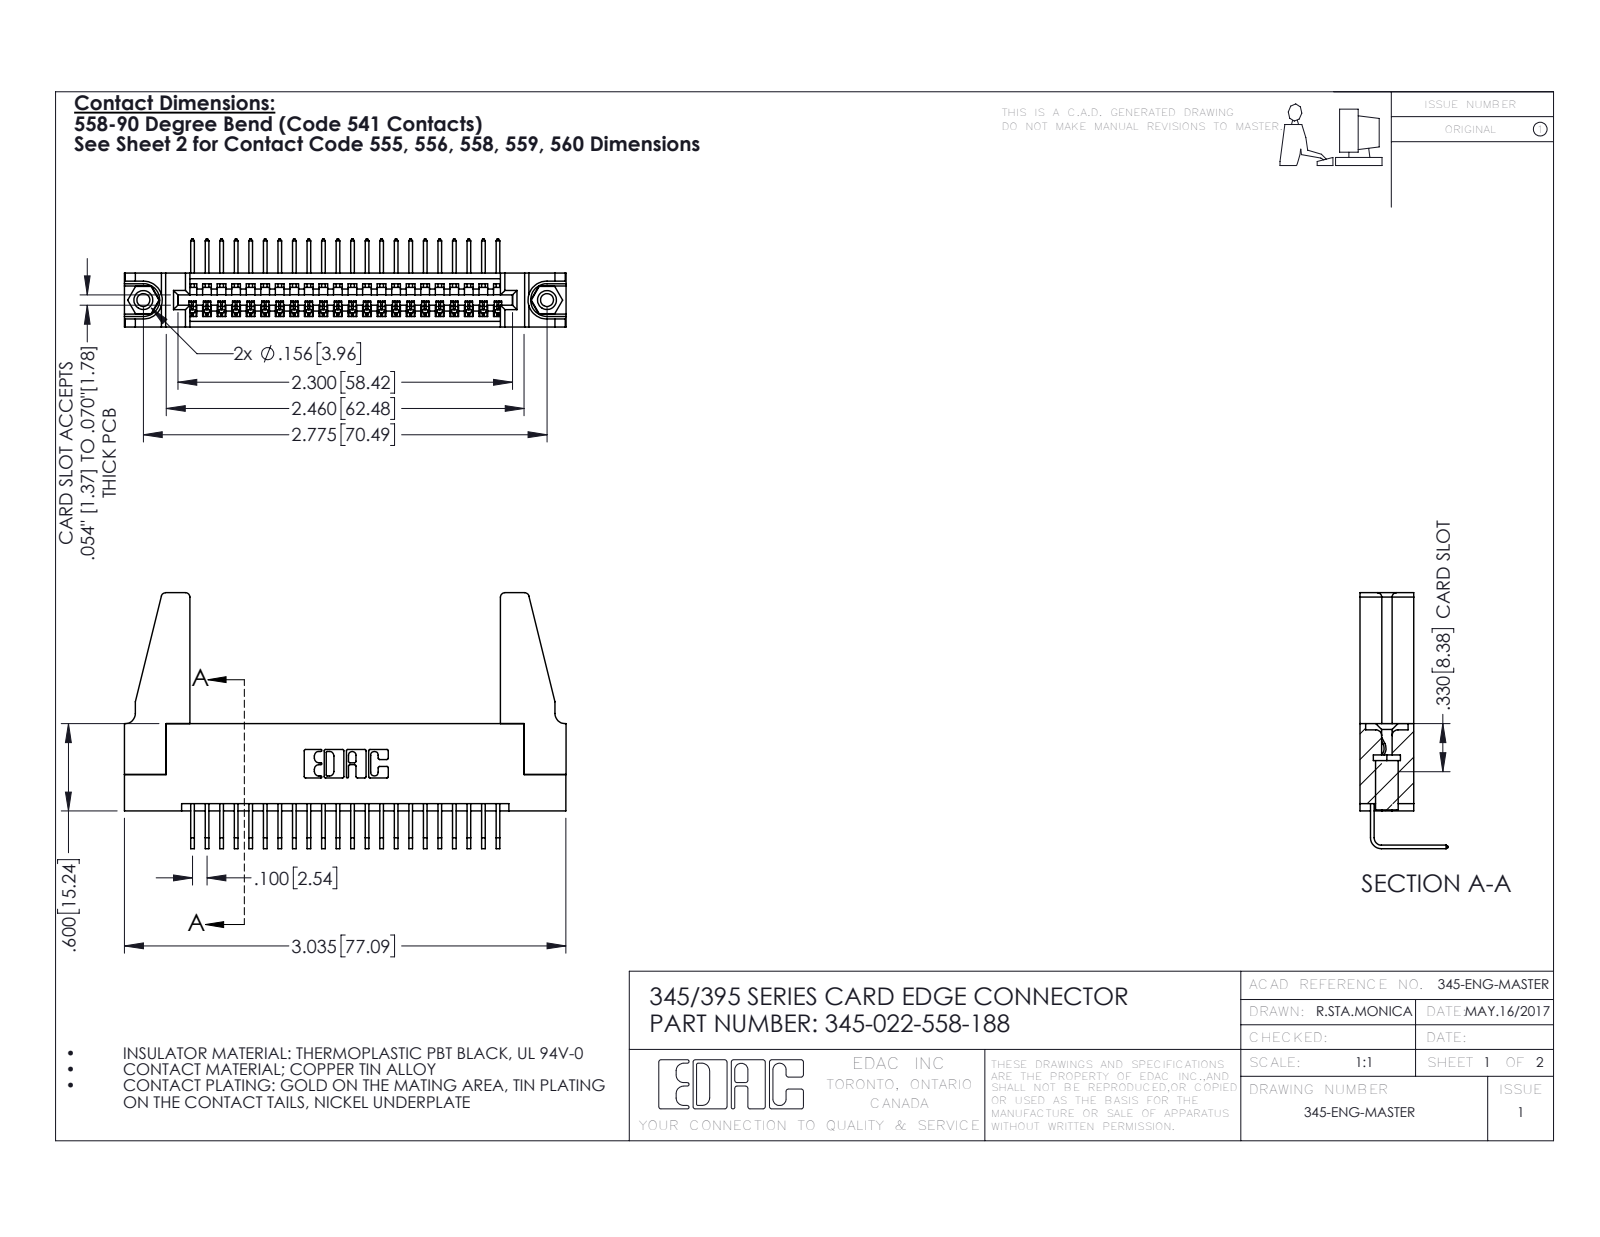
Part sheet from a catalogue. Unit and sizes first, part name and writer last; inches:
Units: inches
Overall size (bounding box): 3.036 × 1.759 × 0.605
Round holes (diameter × count): ⌀0.089 ×2, ⌀0.125 ×2, ⌀0.156 ×2, ⌀0.064 ×1
Round bosses / shafts (diameter × count): ⌀0.155 ×2
Partial cylindrical surfaces — rounded edges, fillets, slot ends (radius × count): R0.006 ×44, R0.01 ×22, R0.03 ×8, R0.007 ×6, R0.031 ×6, R0.026 ×3, R0.031 ×2, R0.04 ×2
Main face-to-face distances: 0.37, 0.072, 0.298, 0.2, 0.098, 0.272, 0.025, 0.225, 0.149, 0.15
Hole centre spacings: 0.27, 2.541, 2.775
Volume: 0.64 in³ · Surface area: 20 in²
Bodies: 27 solids, 1570 faces (1076 planar, 478 cylindrical, 16 other)
Part name (STEP PRODUCT): 345-250-001_345-250-001-102; 345-292-001_558 Tail - 2; 345 Part_Flush Mounting Lugs - 0.156 Dia-TH; 345-022-558-188 (+1 more)
STEP written by: SolidWorks 2016 (CONFIG_CONTROL_DESIGN)
